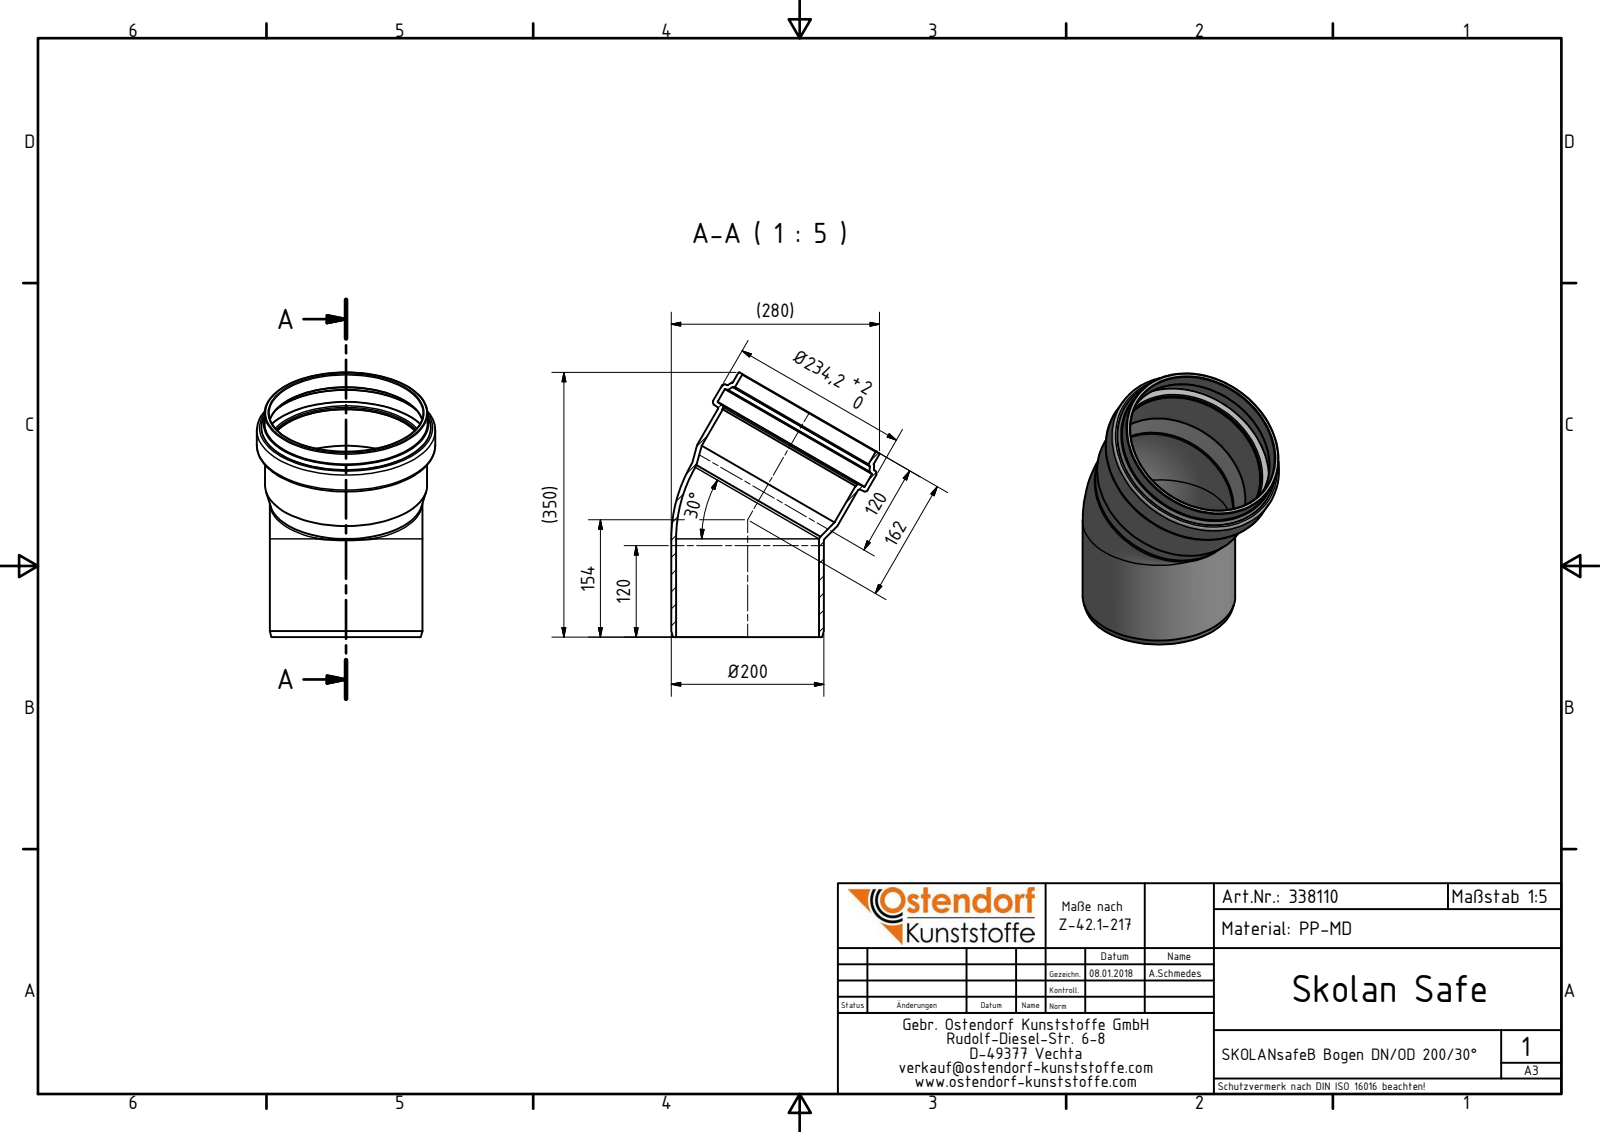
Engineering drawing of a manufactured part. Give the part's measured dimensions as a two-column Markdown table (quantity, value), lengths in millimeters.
| quantity | value |
| --- | --- |
| part name | 338110 SKOLANsafeB Bogen DN_OD 200_30° |
| STEP written by | Autodesk Inventor 2016 (AUTOMOTIVE_DESIGN) |
| units | millimeters |
| bodies | 1 solid, 41 faces (3 planar, 11 cylindrical, 27 other) |
| overall size | 347.36 × 273.32 × 234.2 |
| volume | 1 193 000 mm³ |
| surface area | 424 287 mm² |
| round holes (diameter × count) | 187.9 × 2, 201.5 × 1, 202.5 × 1, 223 × 1 |
| round bosses / shafts (diameter × count) | 200.3 × 2, 234.2 × 1, 213.7 × 1, 212.7 × 1 |
| main face-to-face distances | 52.89 |
